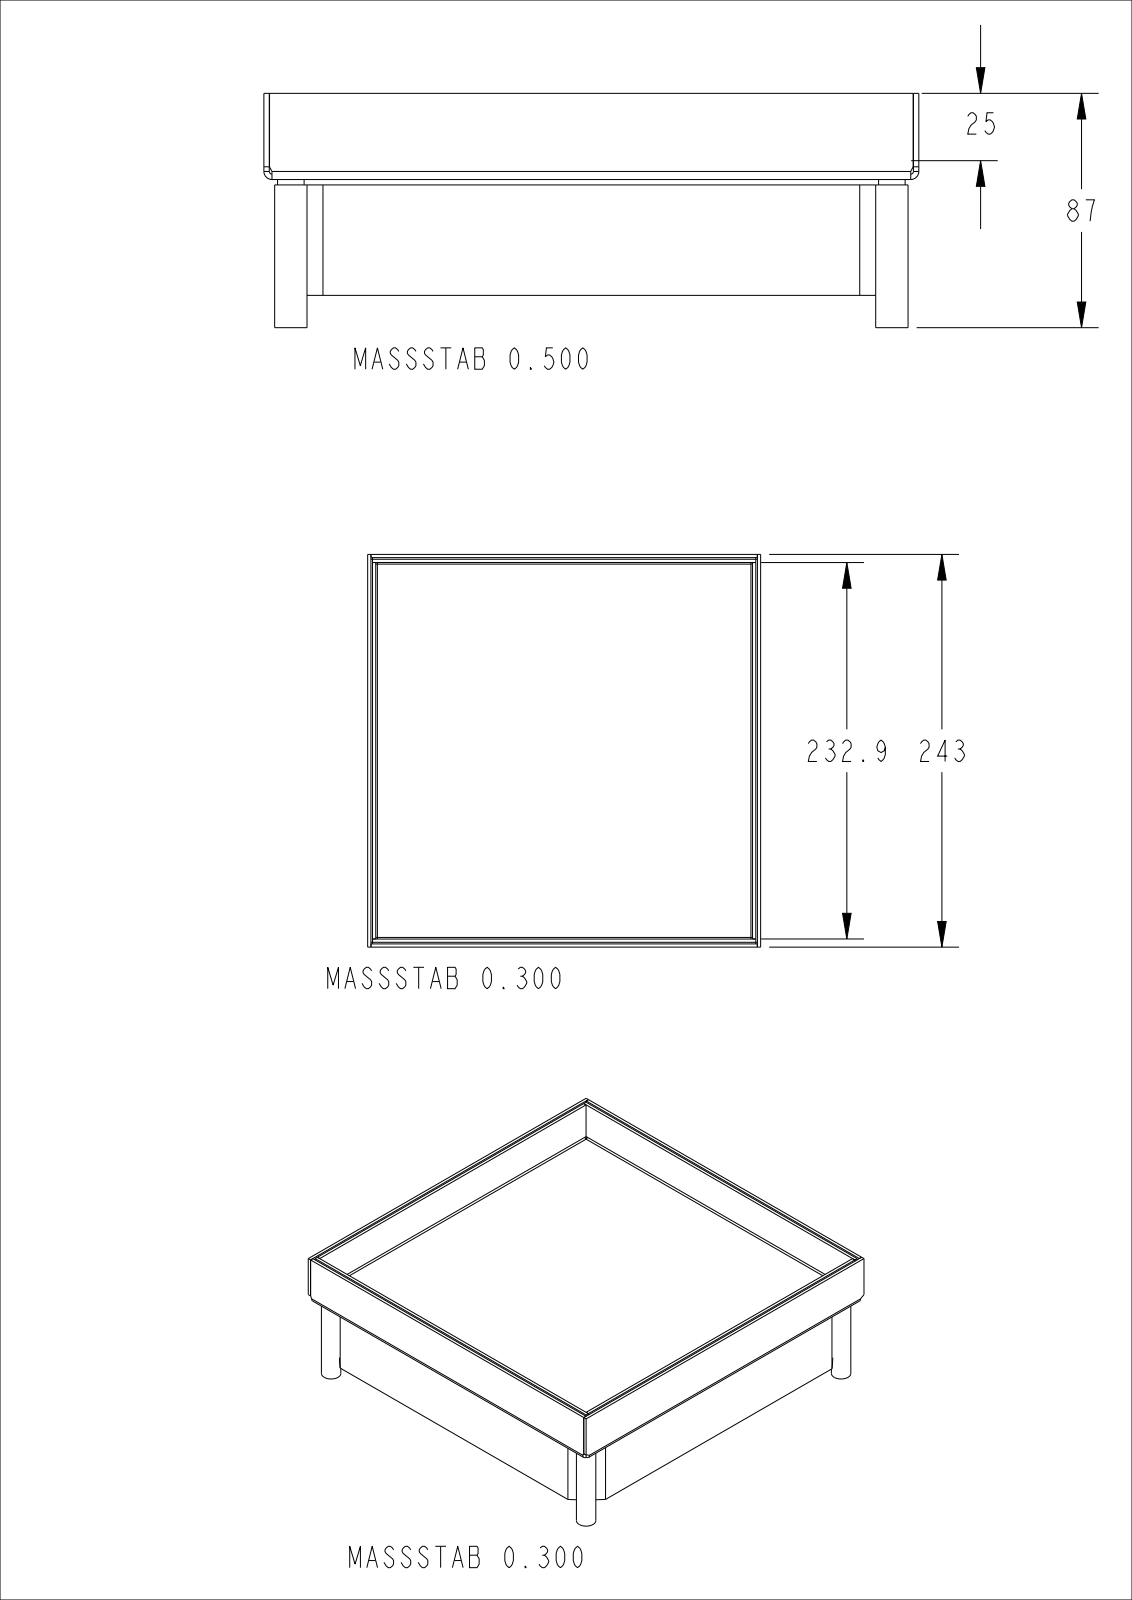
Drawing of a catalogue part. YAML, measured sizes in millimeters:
part_name: "T-00627_1; T-00632_1_1; T-00625_1_1; T-00824_ASM_1_ASM (+4 more)"
step_written_by: "CREO PARAMETRIC BY PTC INC, 2022281 (AUTOMOTIVE_DESIGN)"
units: millimeters
bodies: {solids: 7, faces: 166, planar: 110, cylindrical: 56, other: 0}
overall_size: [243, 243, 87]
volume: 333696
surface_area: 328773
round_holes:
  - {diameter: 6.8, count: 4}
  - {diameter: 8.5, count: 4}
round_bosses_or_shafts:
  - {diameter: 12, count: 4}
  - {diameter: 9.85, count: 4}
partial_cylinders:
  - {radius: 1, count: 8}
  - {radius: 3, count: 8}
  - {radius: 150, count: 1}
  - {radius: 152.5, count: 1}
face_to_face_distances: [2, 3, 235, 238, 5, 2.5, 1, 232, 6, 241]
hole_center_spacings: [223, 315.37]
